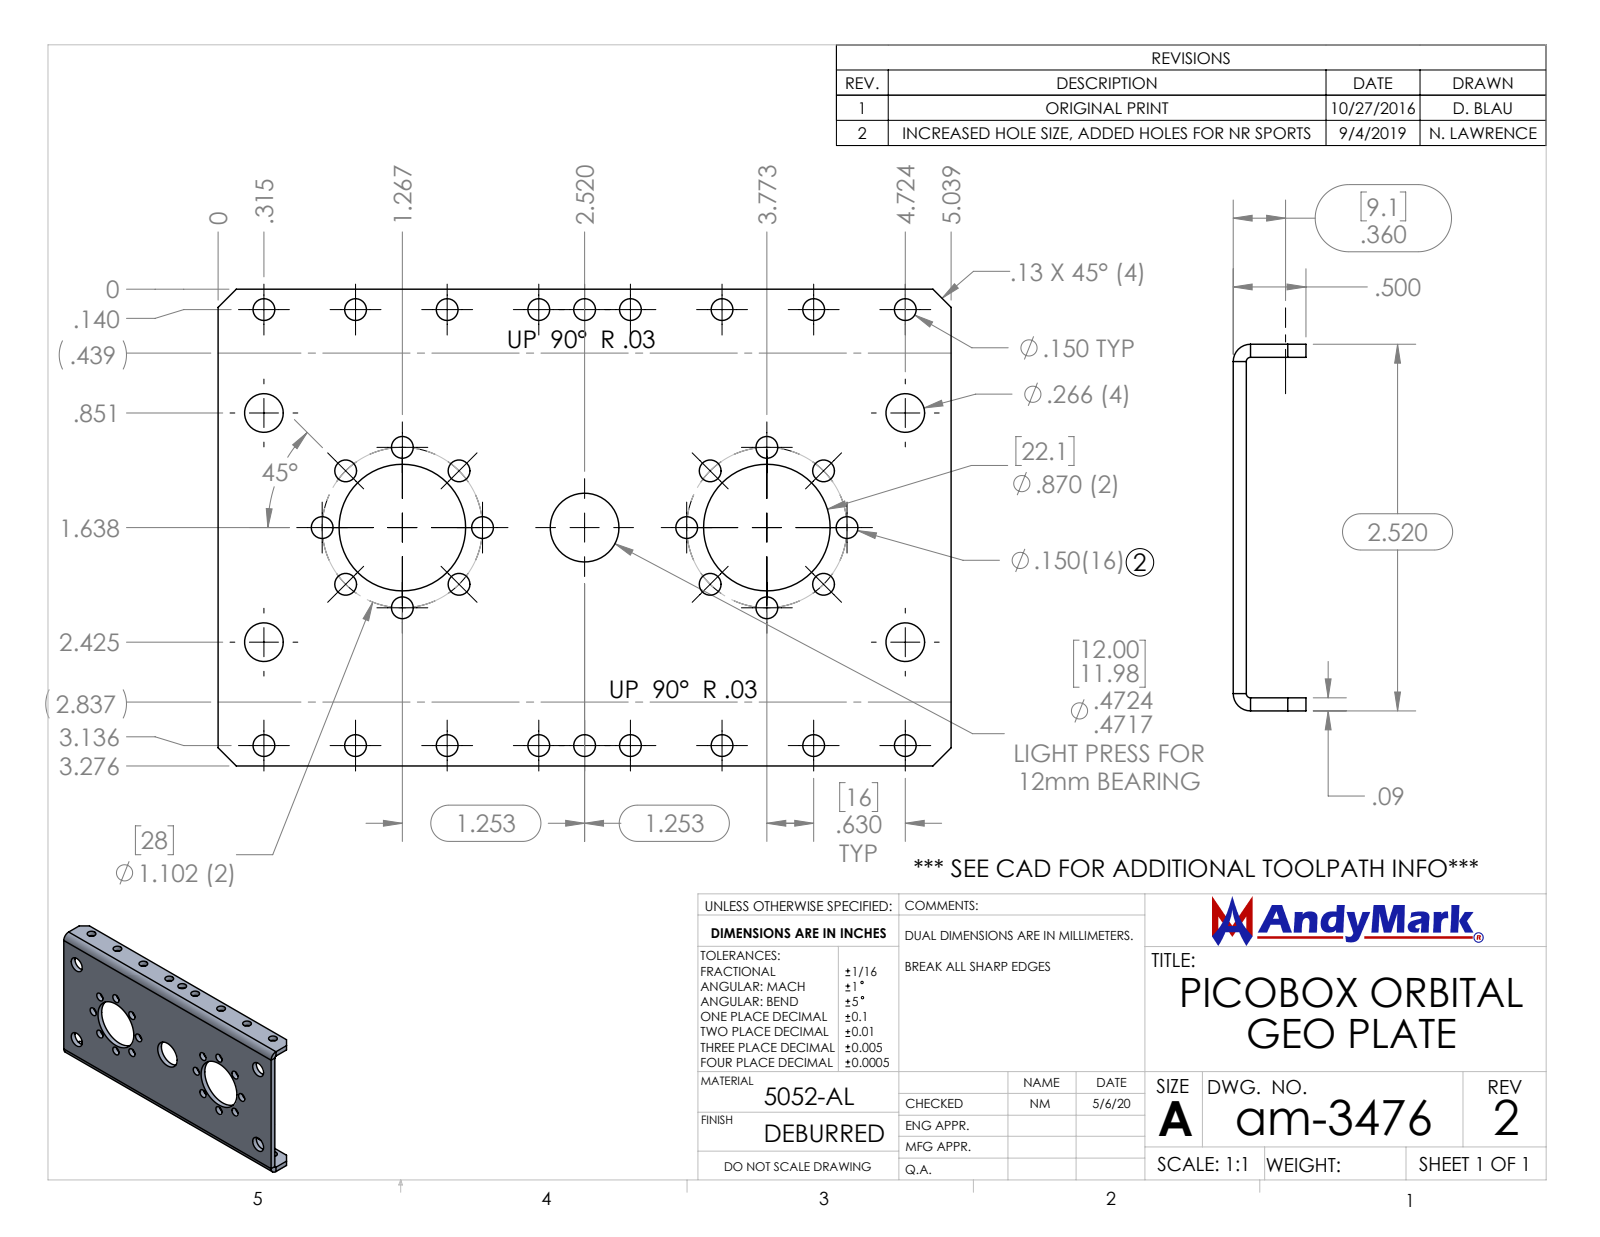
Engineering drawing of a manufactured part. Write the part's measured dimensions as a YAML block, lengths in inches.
part_name: "am-3476 PicoBox Orbital GEO Plate"
step_written_by: "SolidWorks 2019 (AUTOMOTIVE_DESIGN)"
units: inches
bodies: {solids: 1, faces: 67, planar: 22, cylindrical: 45, other: 0}
overall_size: [5.039, 2.52, 0.5]
volume: 1.286
surface_area: 32.42
round_holes:
  - {diameter: 0.15, count: 25}
  - {diameter: 0.266, count: 4}
  - {diameter: 0.87, count: 2}
  - {diameter: 0.472, count: 1}
partial_cylinders:
  - {radius: 0.029, count: 2}
  - {radius: 0.119, count: 2}
face_to_face_distances: [0.09, 2.43, 2.52, 2.339, 0.41, 0.5, 5.039]
hole_center_spacings: [0.422, 0.551, 0.78, 1.019, 2.506, 1.102, 0.63, 1.26]
